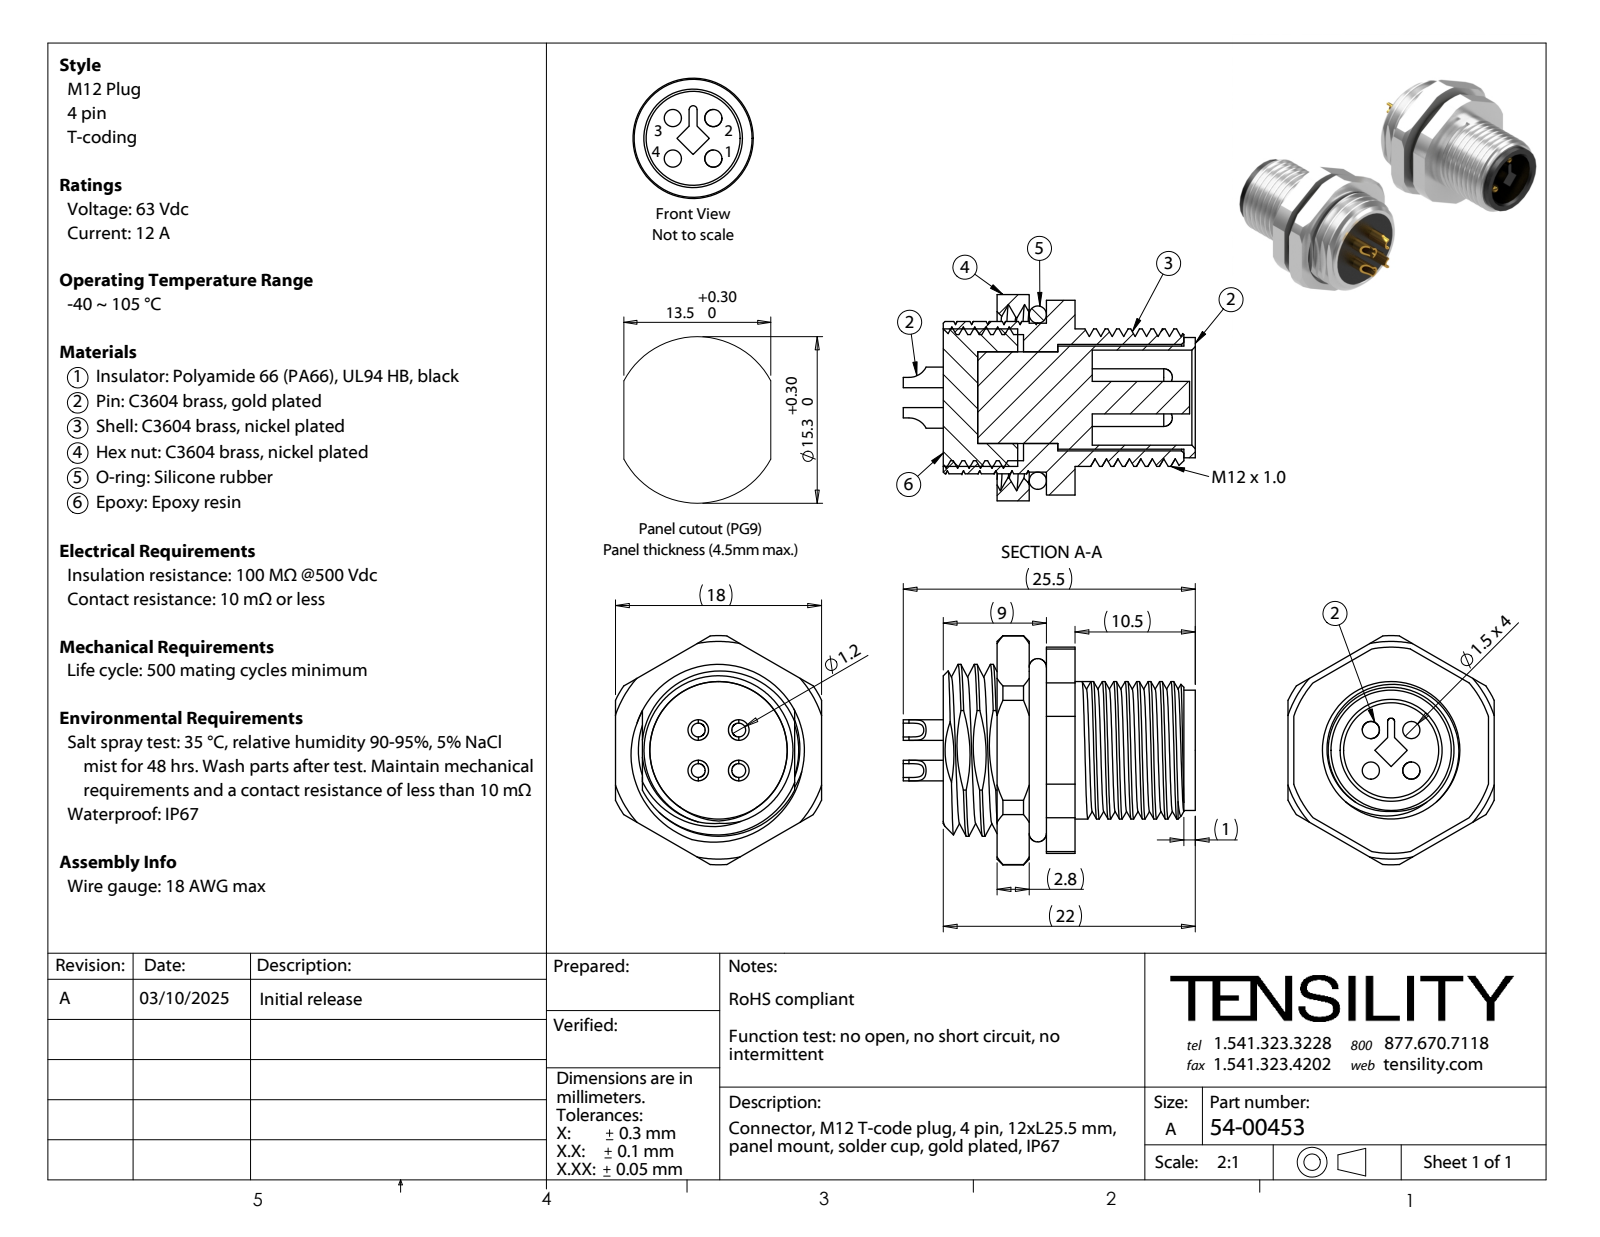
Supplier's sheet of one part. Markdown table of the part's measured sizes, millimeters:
| quantity | value |
| --- | --- |
| part name | 54-00453-02; 54-00453-04; 54-00453; 54-00453-01 (+3 more) |
| STEP written by | SolidWorks 2021 (CONFIG_CONTROL_DESIGN) |
| units | millimeters |
| bodies | 9 solids, 332 faces (84 planar, 154 cylindrical, 94 other) |
| overall size | 25.5 × 20 × 18 |
| volume | 2 978 mm³ |
| surface area | 5 771 mm² |
| round holes (diameter × count) | 1.2 × 4, 1.5 × 4, 8 × 1, 8.3 × 1, 9.3 × 1, 11 × 1, 14 × 1 |
| round bosses / shafts (diameter × count) | 1.8 × 4, 13 × 1, 12 × 1, 10.5 × 1, 9 × 1 |
| partial cylindrical surfaces (radius × count) | 1.7 × 2, 0.3 × 1, 7.5 × 1, 9 × 1, 10 × 1 |
| main face-to-face distances | 4, 2.5, 0.5, 1.5, 3, 9, 11.5, 6, 4.5, 1 |
| hole center spacings | 2.5, 3.54, 5.01 |
